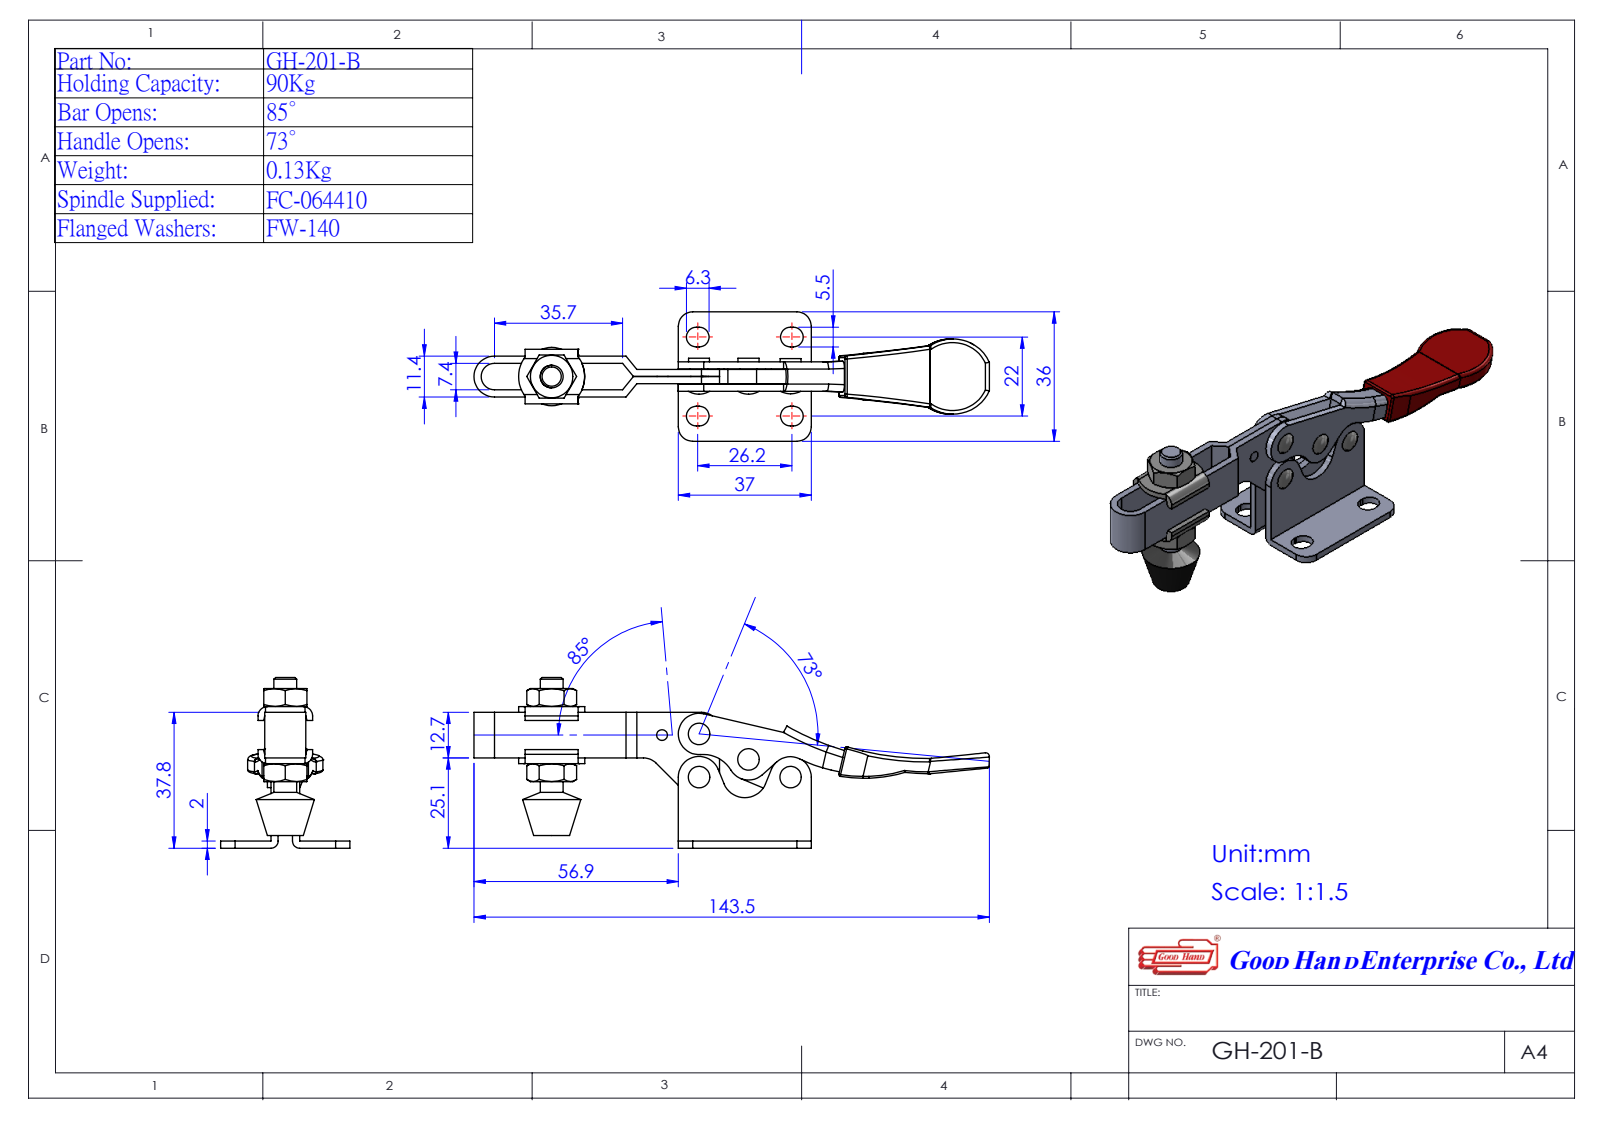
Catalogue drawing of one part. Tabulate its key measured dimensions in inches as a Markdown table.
| quantity | value |
| --- | --- |
| part name | Group6^EMC201B; Group5^EMC201B; EMC201B; 1201B05-1^EMC201B (+2 more) |
| STEP written by | SolidWorks 2016 (AUTOMOTIVE_DESIGN) |
| units | inches |
| bodies | 5 solids, 249 faces (112 planar, 112 cylindrical, 25 other) |
| overall size | 5.65 × 1.871 × 1.417 |
| volume | 1.218 in³ |
| surface area | 28.82 in² |
| round holes (diameter × count) | 0.157 × 4 |
| round bosses / shafts (diameter × count) | 0.23 × 4, 0.191 × 2, 0.25 × 1 |
| partial cylindrical surfaces (radius × count) | 0.108 × 8, 0.226 × 5, 0.039 × 4, 0.102 × 4, 0.157 × 4, 3.15 × 3, 0.197 × 2, 0.224 × 2 |
| main face-to-face distances | 0.079, 0.157, 0.067, 0.146, 0.224, 0.303, 0.063, 0.236, 0.307, 0.083 |
| hole center spacings | 0.472, 0.5, 0.576, 0.61, 1.004, 1.109 |
